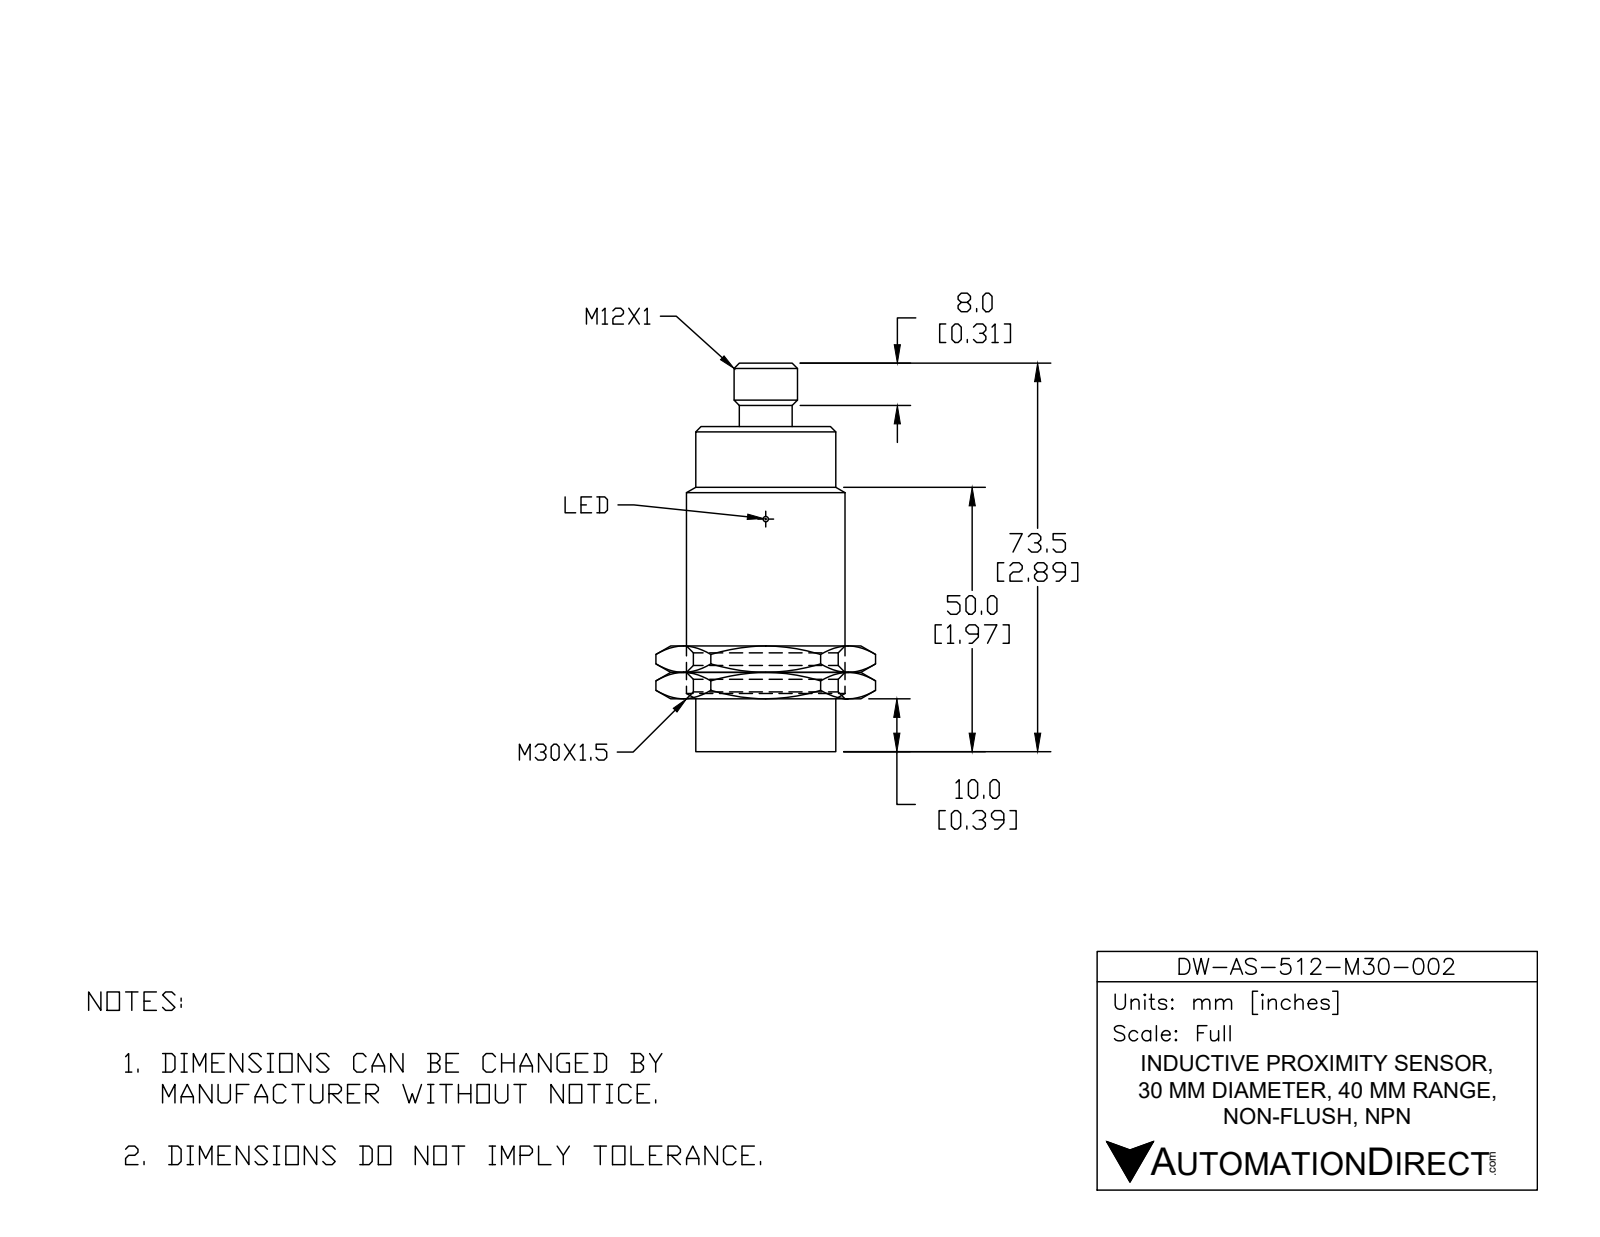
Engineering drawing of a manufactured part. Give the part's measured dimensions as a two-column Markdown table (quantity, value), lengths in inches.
| quantity | value |
| --- | --- |
| part name | DW-AS-512-M30-002 |
| STEP written by | SolidWorks 2017 (AUTOMOTIVE_DESIGN) |
| units | inches |
| bodies | 1 solid, 36 faces (13 planar, 14 cylindrical, 9 other) |
| overall size | 2.896 × 1.181 × 1.181 |
| volume | 2.531 in³ |
| surface area | 12.1 in² |
| round holes (diameter × count) | 0.12 × 2, 0.335 × 1 |
| round bosses / shafts (diameter × count) | 0.043 × 3, 1.181 × 1, 1.095 × 1, 1.083 × 1, 0.472 × 1, 0.415 × 1 |
| partial cylindrical surfaces (radius × count) | 0.019 × 2, 0.022 × 1 |
| main face-to-face distances | 2.382, 2.553, 0.171, 2.047, 0.335, 0.506, 0.394, 1.654, 1.988, 2.159 |
